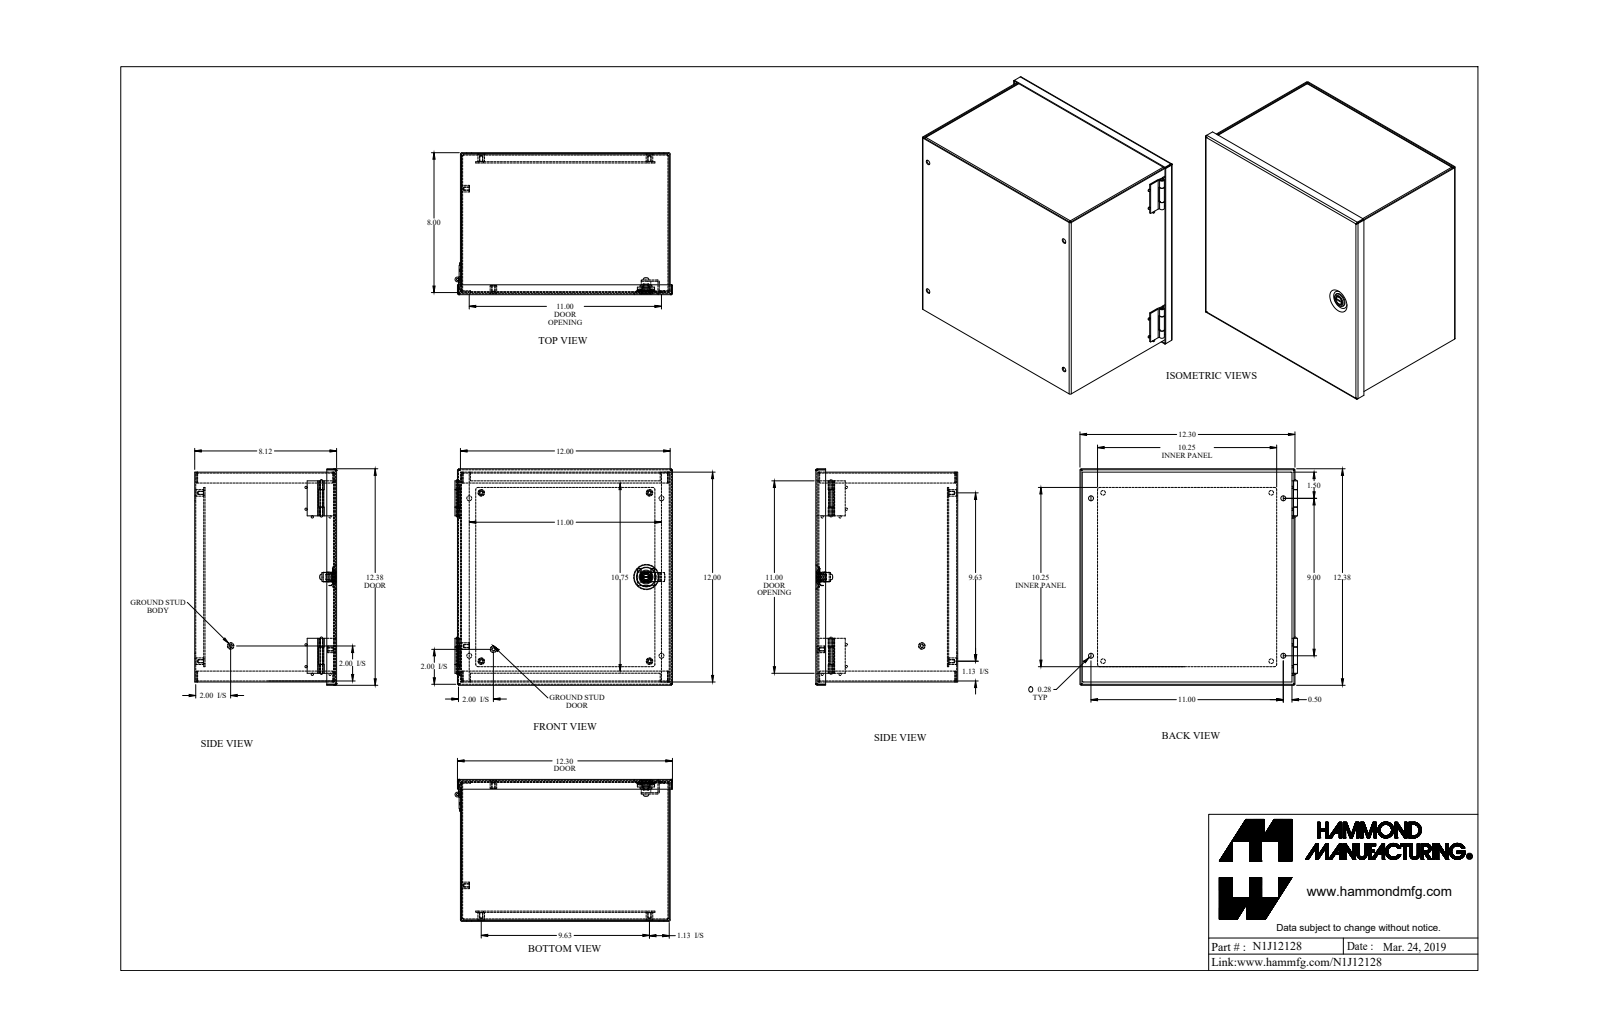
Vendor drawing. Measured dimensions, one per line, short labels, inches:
name: N1J12128
written by: SolidWorks 2018 (AUTOMOTIVE_DESIGN)
unit: in
bodies: 18 solids, 477 faces (224 planar, 188 cylindrical, 65 other)
size: 12.443 × 12.38 × 8.118
volume: 51.27 in³; area: 1 750 in²
holes: 6× ⌀0.156, 4× ⌀0.265, 4× ⌀0.28, 1× ⌀0.125, 1× ⌀0.319, 1× ⌀0.476
bosses: 8× ⌀0.131, 6× ⌀0.375, 1× ⌀0.787, 1× ⌀0.547, 1× ⌀0.472, 1× ⌀0.469, 1× ⌀0.366, 1× ⌀0.32
rounds: 16× R0.029, 16× R0.086, 4× R0.012, 4× R0.1, 4× R0.125, 2× R0.036, 2× R0.079, 2× R0.25
face distances: 0.057, 11.943, 8.061, 12, 11.886, 8.004, 8.118, 0.072, 0.517, 0.46
hole spacings: 0.755, 9.338, 9.625, 10.317, 13.895, 4.586, 4.817, 9
